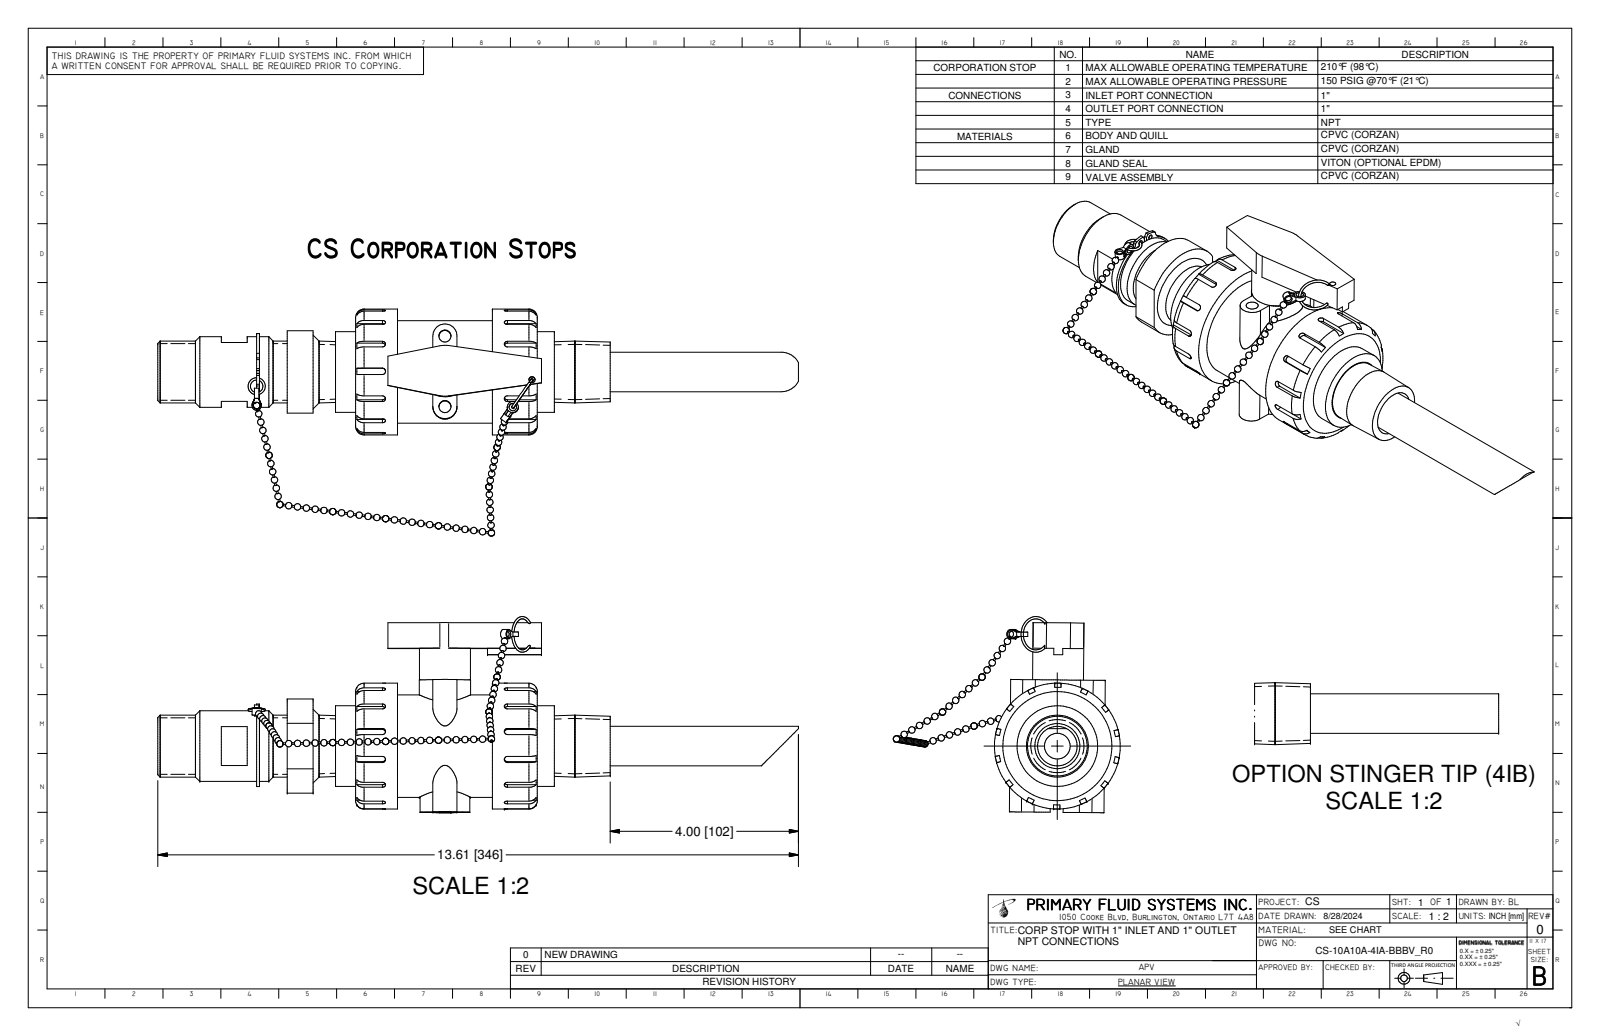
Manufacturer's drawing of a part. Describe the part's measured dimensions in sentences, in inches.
Its 3-D file was written by "Autodesk Inventor 2025 (CONFIG_CONTROL_DESIGN)". It is 19 solids with 420 faces: 205 planar, 137 cylindrical and 78 other. Overall it measures 13.613 by 4.823 by 4.168 inches. Its volume is 29.93 cubic inches and its surface area 176.3 square inches. Round holes: 2 of diameter 0.098, 2 of diameter 0.15, 2 of diameter 0.157, 2 of diameter 0.256, 1 of diameter 0.13, 1 of diameter 0.546, 1 of diameter 0.818, 1 of diameter 0.875, 1 of diameter 0.957, 1 of diameter 1.306, 1 of diameter 1.315, 1 of diameter 1.386. Round bosses or shafts: 9 of diameter 0.035, 2 of diameter 0.236, 1 of diameter 2.673, 1 of diameter 2.177, 1 of diameter 1.713, 1 of diameter 1.634, 1 of diameter 1.5, 1 of diameter 1.33. Partial cylindrical surfaces (rounded edges, fillets, slot ends): 26 of radius 0.067, 2 of radius 0.054, 2 of radius 0.098, 2 of radius 0.197, 2 of radius 0.256, 1 of radius 0.545, 1 of radius 0.898, 1 of radius 1. The main face-to-face distances are 0.646, 2.661, 1.317, 3.333, 0.672, 3.979, 3.86, 0.89, 2.906, 2.016. The hole center spacings are 0.749, 0.795, 0.295, 0.314, 0.609, 0.708, 0.885, 1.443.
